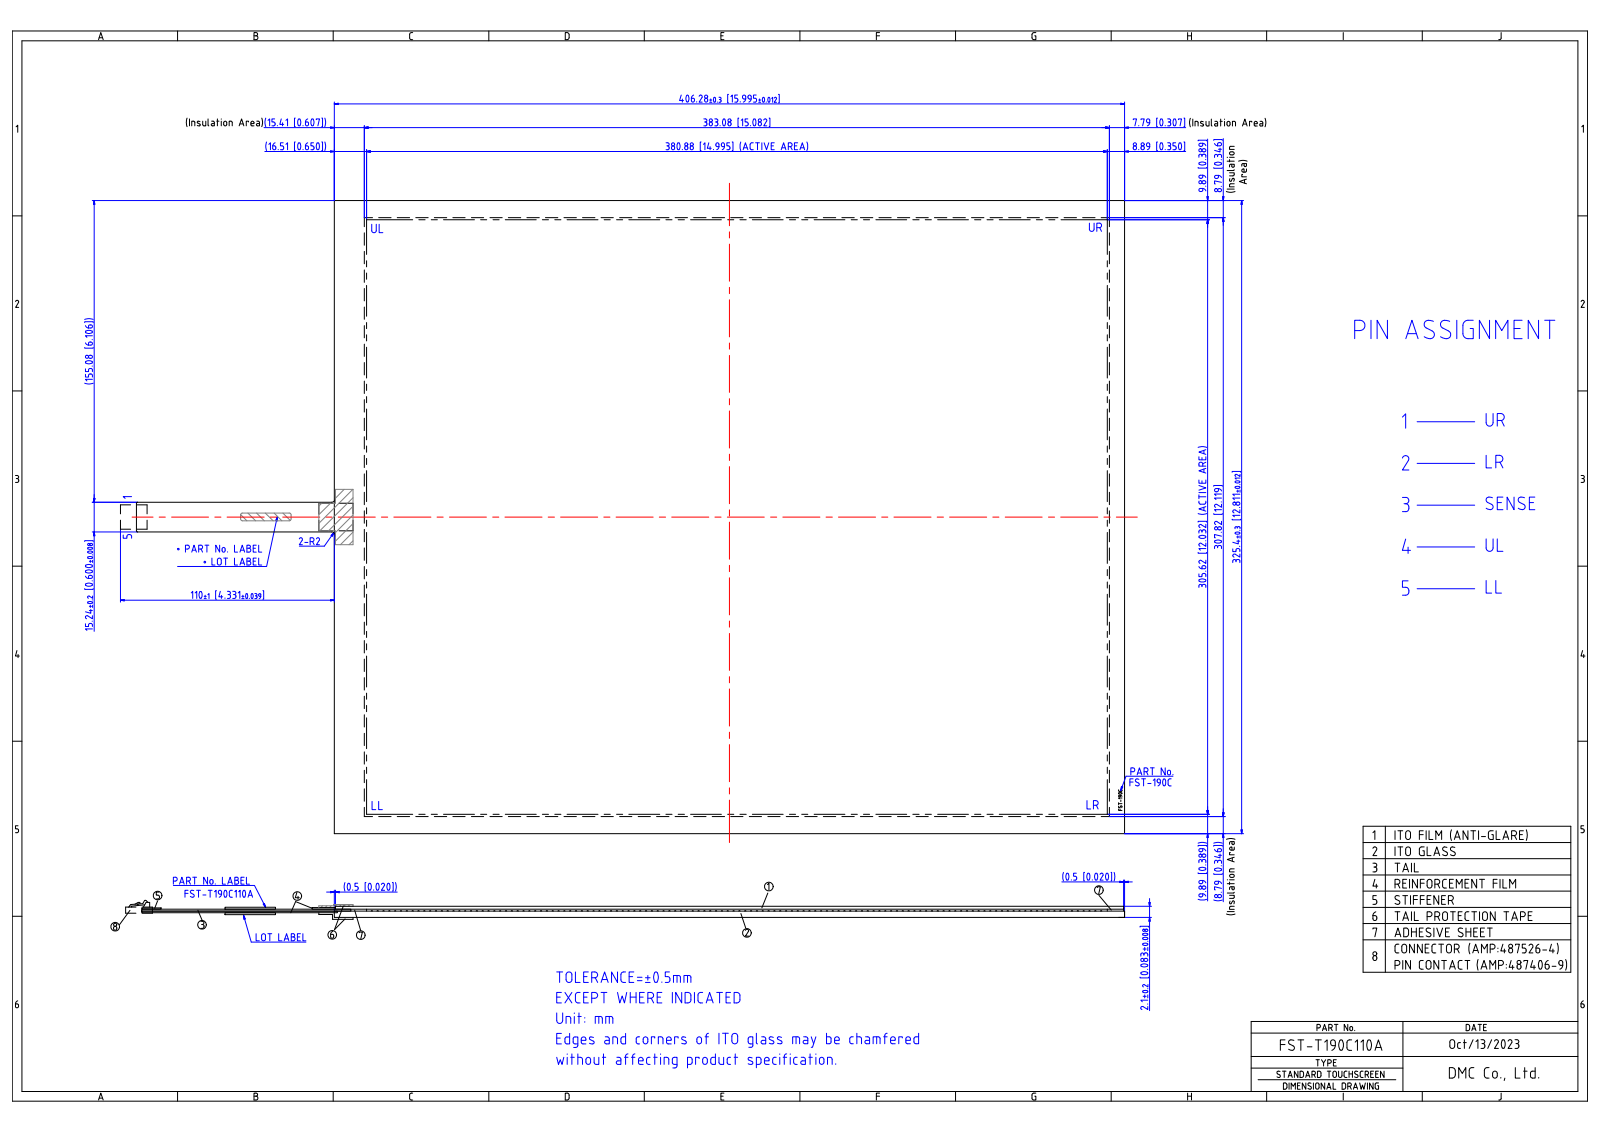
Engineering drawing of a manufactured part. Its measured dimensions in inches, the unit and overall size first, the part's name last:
Units: inches
Overall size (bounding box): 23.526 × 17.935 × 0.124
Main face-to-face distances: 0.079, 0.083, 0.071, 0.075, 12.811, 15.995, 0.026, 0.03, 0.033, 0.045
Volume: 16.26 in³ · Surface area: 420.1 in²
Bodies: 1 solid, 43 faces (43 planar, 0 cylindrical, 0 other)
Part name (STEP PRODUCT): FST-T190C110A
STEP written by: Autodesk Inventor 2020 (AUTOMOTIVE_DESIGN)
